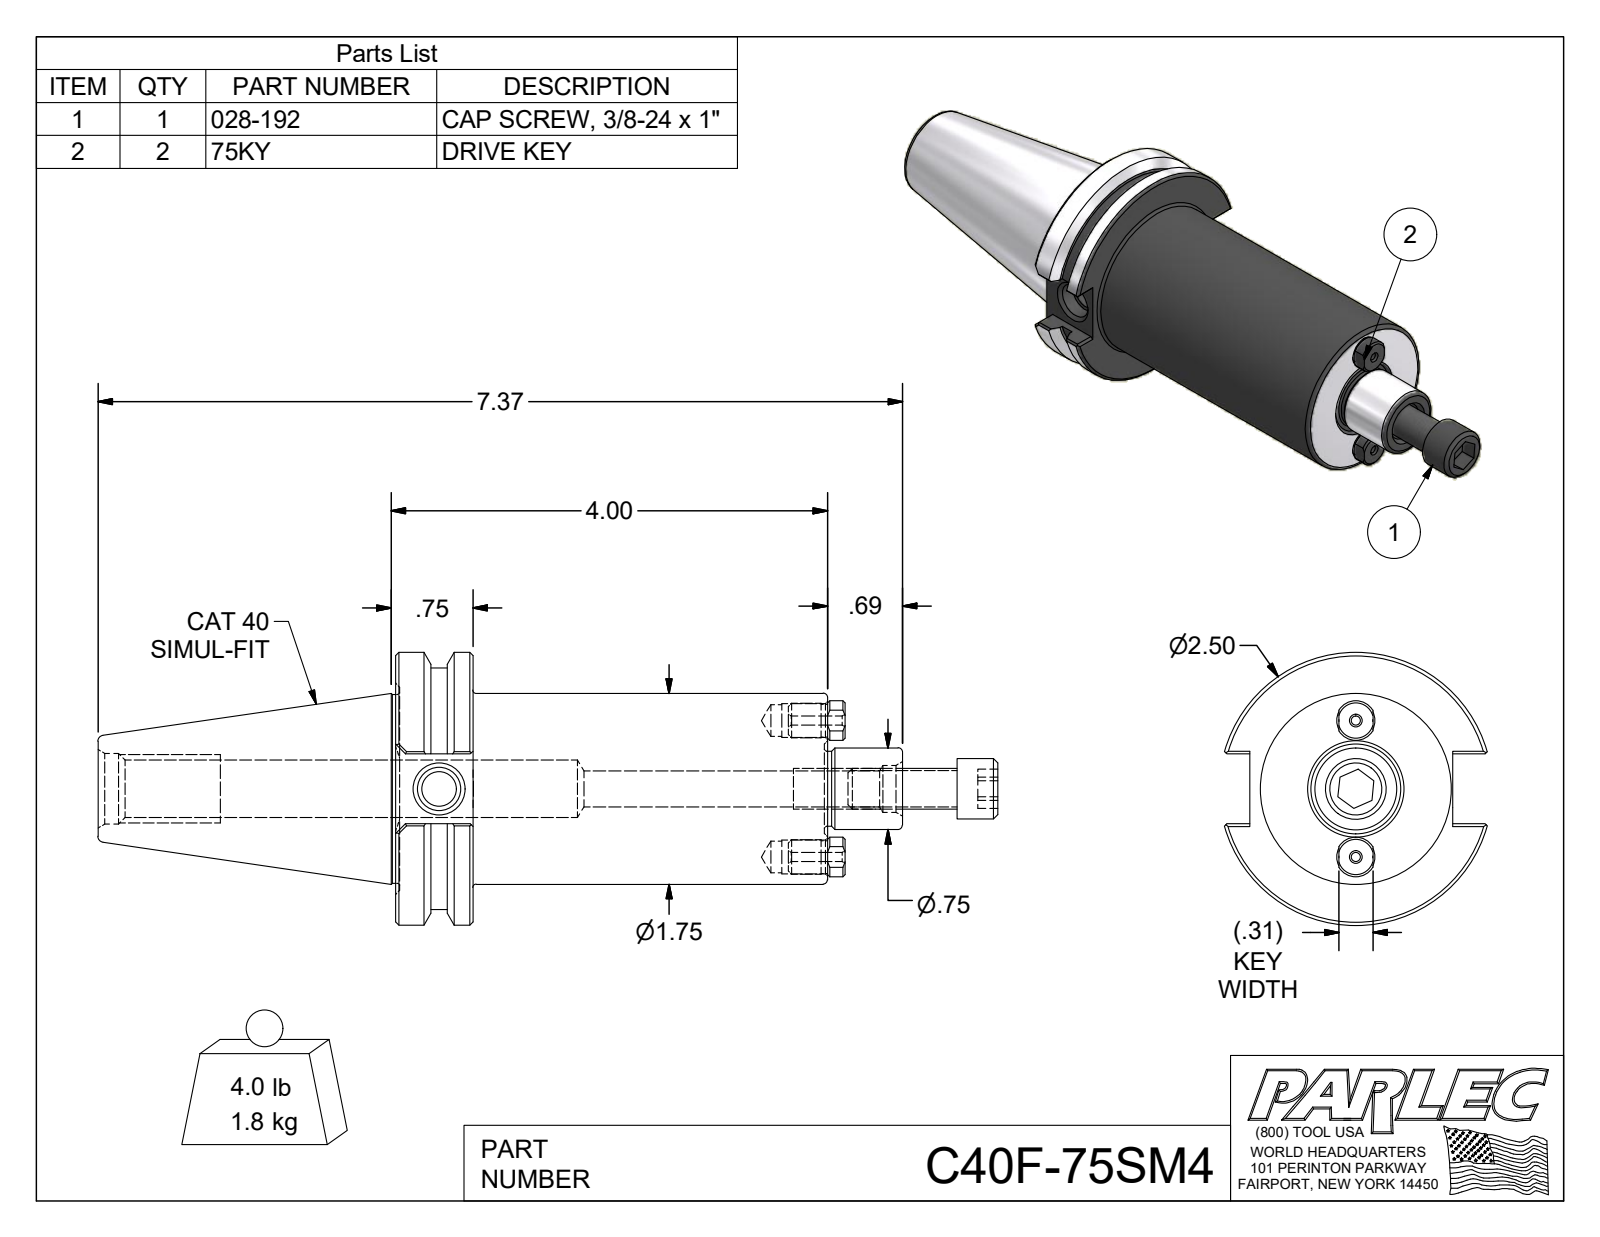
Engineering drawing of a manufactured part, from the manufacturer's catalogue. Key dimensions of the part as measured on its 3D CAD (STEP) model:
Part name (STEP PRODUCT): C40F-75SM4; C40F-75SM4-1; 75KY; 028-192
STEP written by: Autodesk Inventor 2012 (AUTOMOTIVE_DESIGN)
Units: inches
Bodies: 4 solids, 140 faces (58 planar, 32 cylindrical, 50 other)
Overall size (bounding box): 8.246 × 2.5 × 2.406
Volume: 14.1 in³ · Surface area: 61.34 in²
Round holes (diameter × count): ⌀0.084 ×2, ⌀0.292 ×2, ⌀0.312 ×2, ⌀0.315 ×1, ⌀0.33 ×1, ⌀0.399 ×1, ⌀0.43 ×1, ⌀0.527 ×1, ⌀0.648 ×1
Round bosses / shafts (diameter × count): ⌀0.318 ×2, ⌀0.3 ×2, ⌀2.5 ×1, ⌀2.215 ×1, ⌀1.75 ×1, ⌀1.73 ×1, ⌀0.75 ×1, ⌀0.69 ×1
Partial cylindrical surfaces — rounded edges, fillets, slot ends (radius × count): R0.183 ×2
Main face-to-face distances: 3.25, 0.711, 3.961, 1.86, 0.64, 0.037, 0.674, 3.924, 0.5, 2.727
Hole centre spacings: 0.625, 1.25
